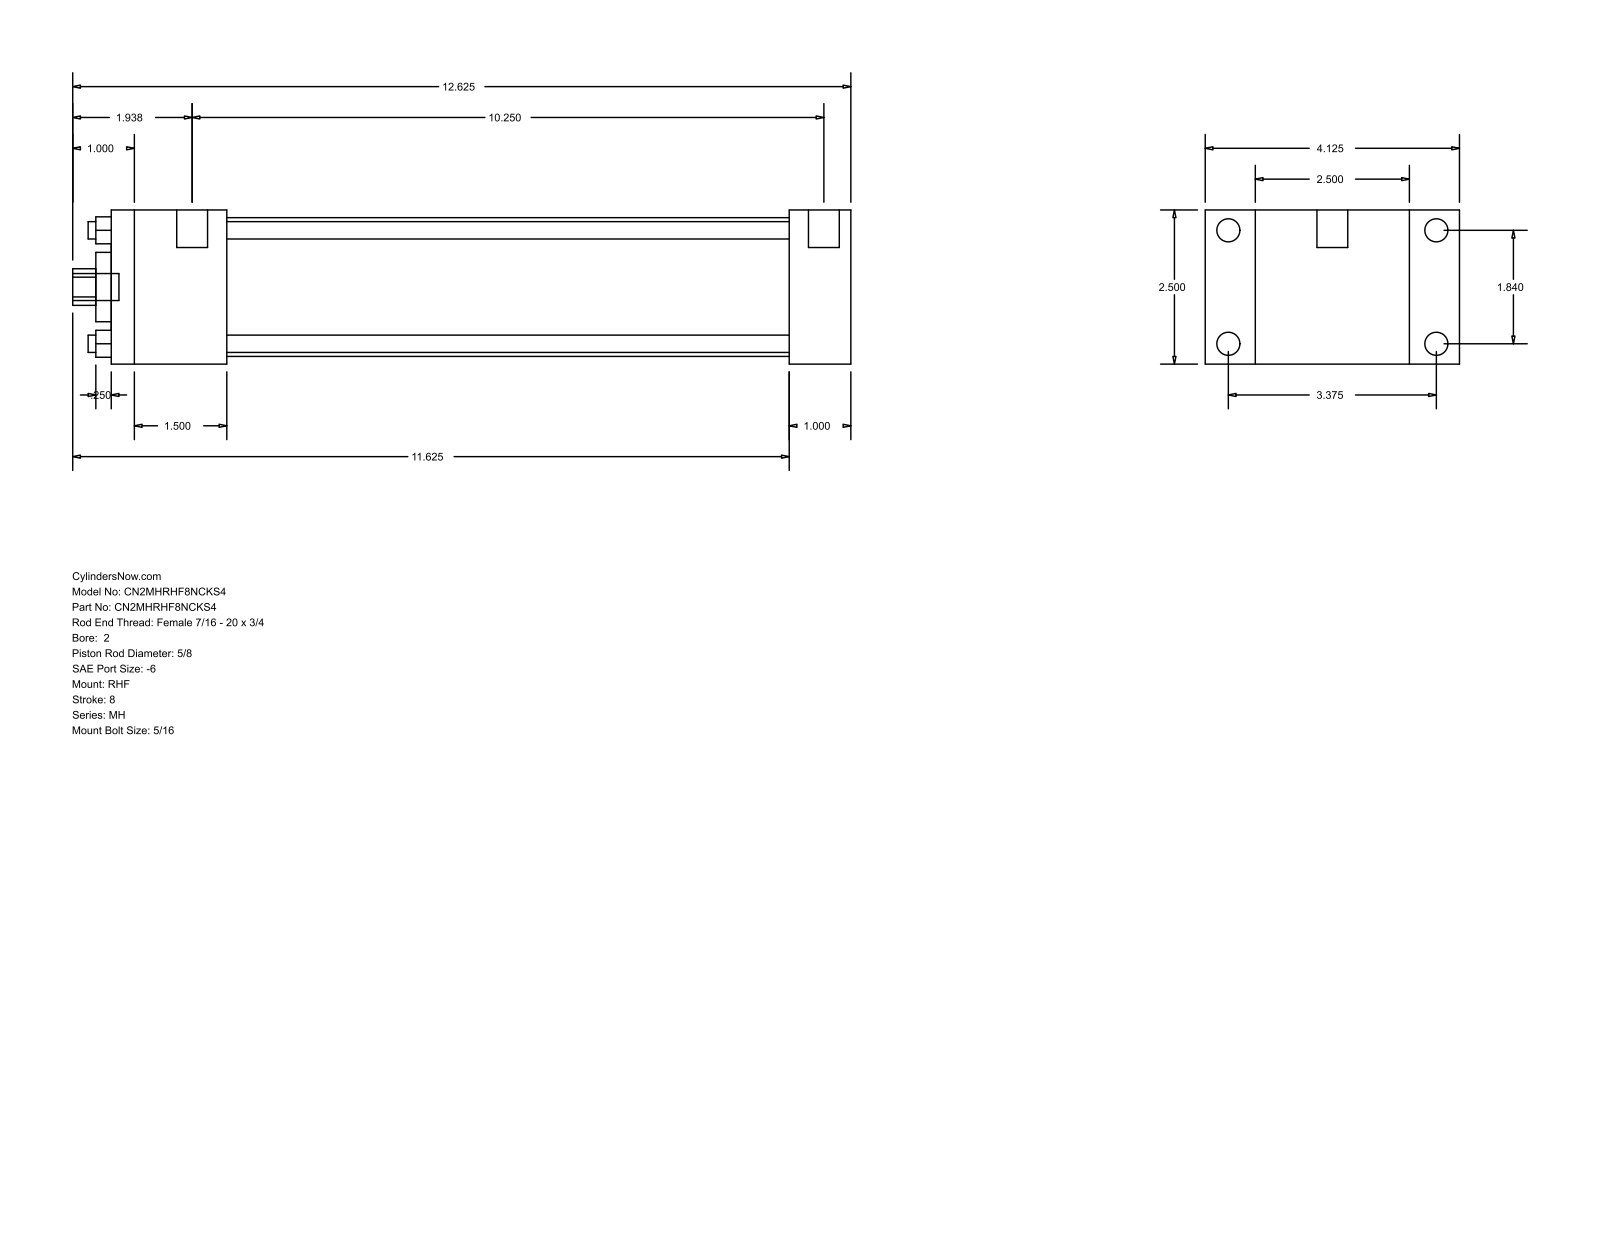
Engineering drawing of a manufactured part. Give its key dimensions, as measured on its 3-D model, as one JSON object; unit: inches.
{"part_name": "MH_RHF__0200_0.625", "step_written_by": "GSSL Pune (CONFIG_CONTROL_DESIGN)", "units": "inches", "bodies": {"solids": 0, "faces": 88, "planar": 60, "cylindrical": 28, "other": 0}, "overall_size": [12.625, 4.125, 2.5], "round_holes": [[0.281, 4], [0.625, 1], [1.125, 1], [2.25, 1]], "round_bosses_or_shafts": [[0.375, 4], [0.219, 4], [0.5, 2], [0.437, 1]], "partial_cylinders_radius": [[0.297, 1]], "face_to_face_distances": [2.5, 1, 0.813, 3.313, 11, 12, 4.125, 1.875, 9.125, 10.125], "hole_center_spacings": [1.301, 1.84, 2.602]}
